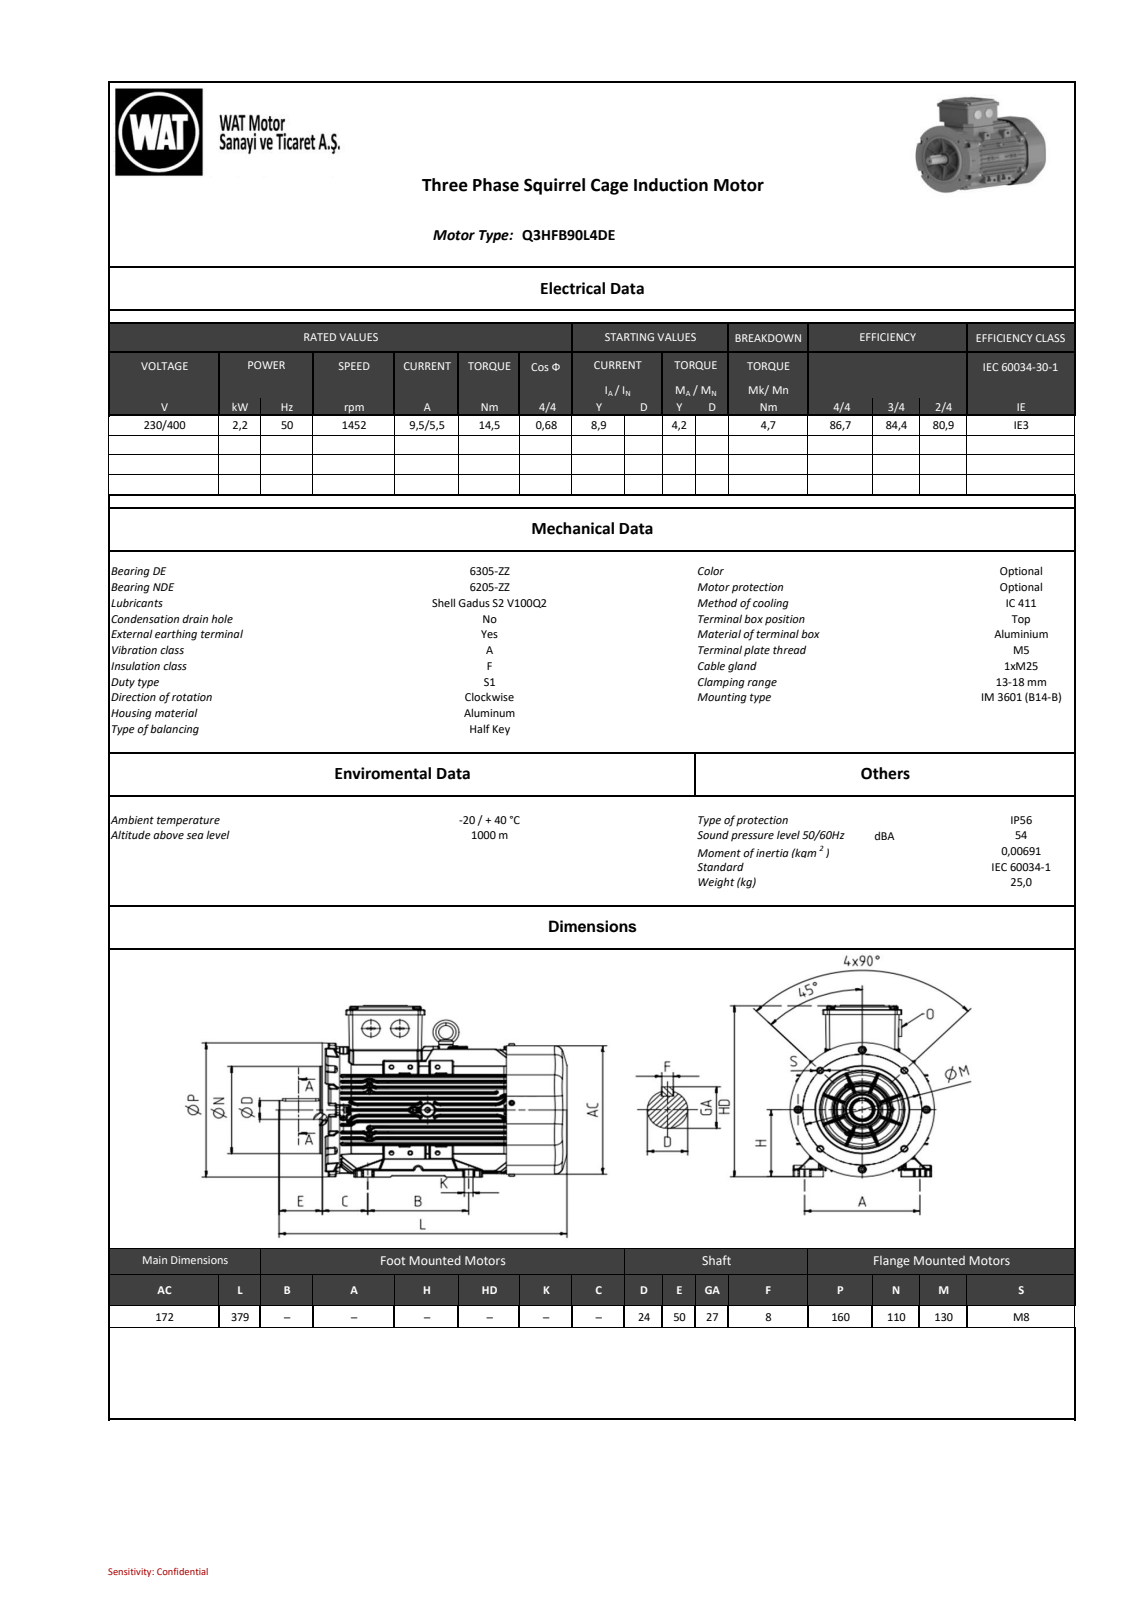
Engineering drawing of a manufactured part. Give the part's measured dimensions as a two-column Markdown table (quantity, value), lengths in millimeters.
| quantity | value |
| --- | --- |
| part name | model1 |
| STEP written by | SIEMENS PLM Software NX2206.8101 (AUTOMOTIVE_DESIGN) |
| units | millimeters |
| bodies | 0 solids, 11470 faces (2460 planar, 3321 cylindrical, 5689 other) |
| overall size | 378.54 × 220.68 × 175.26 |
| round holes (diameter × count) | 5 × 12, 3.5 × 6, 6.8 × 5, 3.3 × 4, 4.72 × 2, 23.38 × 2, 4 × 1, 8.4 × 1, 9.87 × 1, 25.2 × 1, 27.3 × 1, 28.3 × 1 |
| round bosses / shafts (diameter × count) | 8 × 6, 4 × 6, 25 × 3, 5 × 2, 3.87 × 2, 3.24 × 2, 110 × 1, 102.19 × 1 |
| partial cylindrical surfaces (radius × count) | 0.8 × 712, 1 × 702, 0.5 × 344, 2 × 117, 0.25 × 32, 8 × 30, 0.3 × 28, 4 × 12 |
| main face-to-face distances | 7.5, 91.91, 82.98, 8.93, 23.57, 50.35, 1.25, 7.37, 90.35, 16.87 |
| hole center spacings | 79.51, 12.73, 56.8, 65, 70, 88, 91.93, 111.72 |
